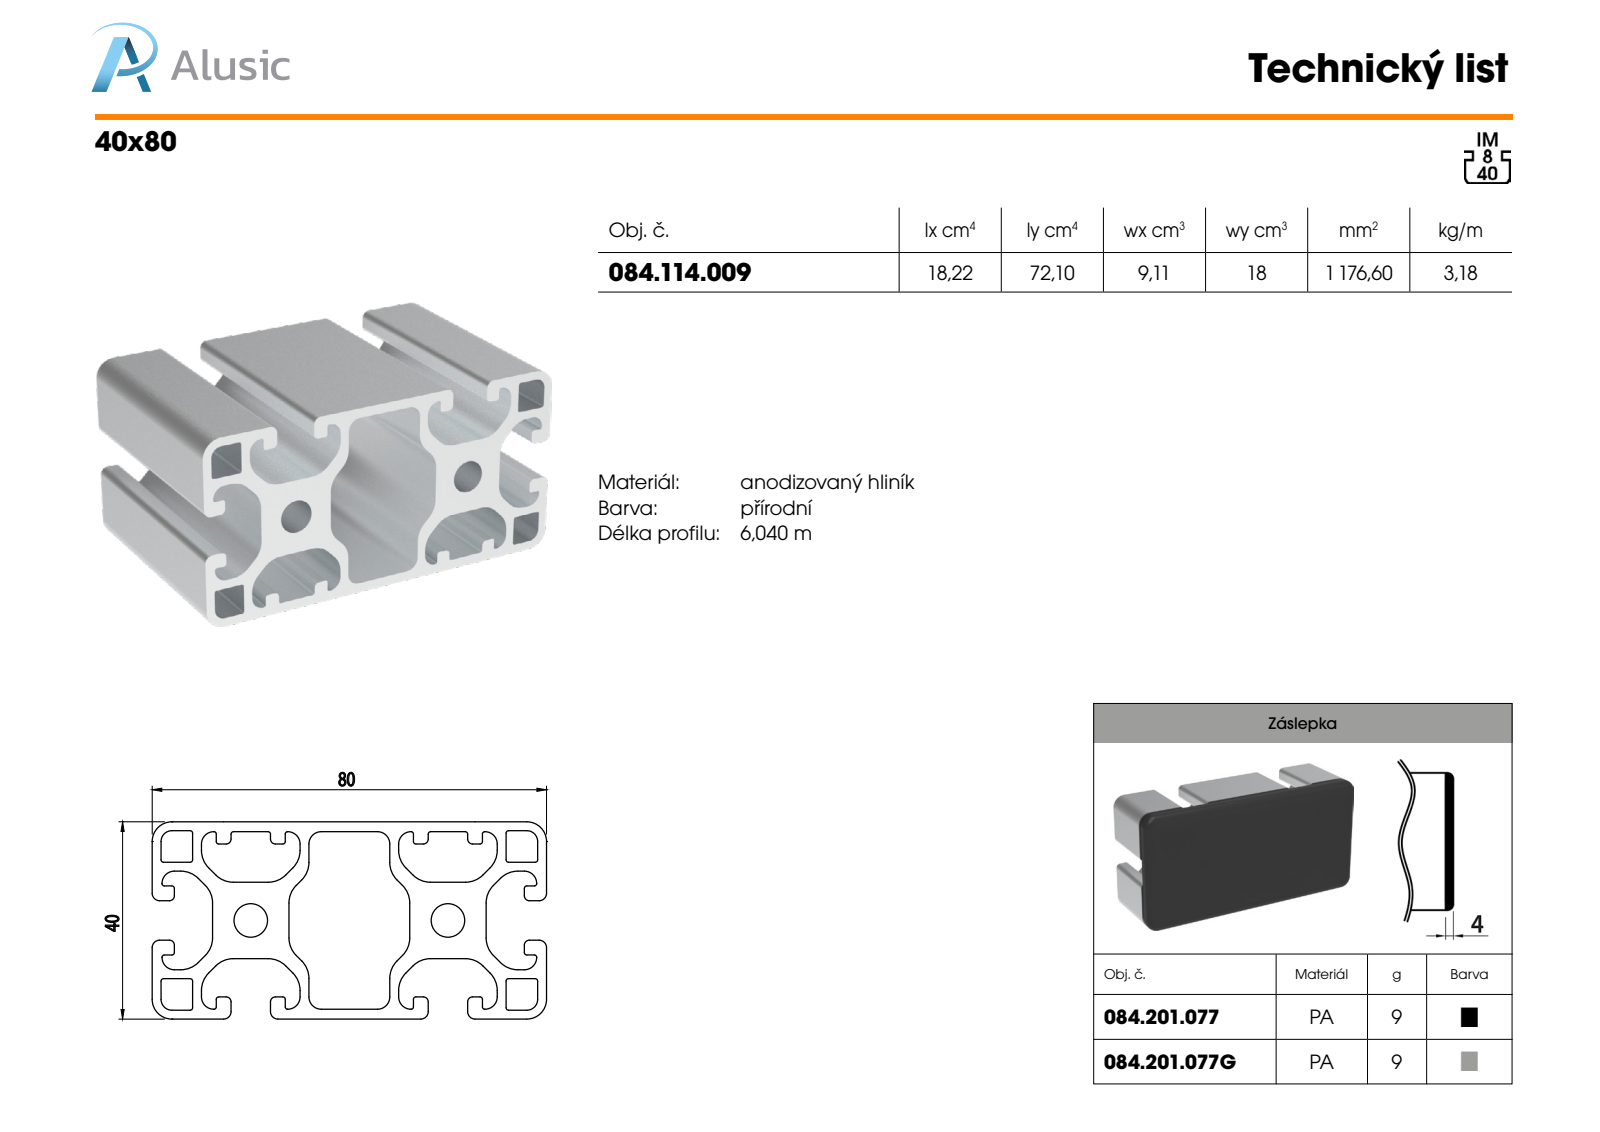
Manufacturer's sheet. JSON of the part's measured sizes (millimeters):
{"part_name": "084.114.009", "step_written_by": "SolidWorks 2018 (AUTOMOTIVE_DESIGN)", "units": "millimeters", "bodies": {"solids": 1, "faces": 238, "planar": 117, "cylindrical": 121, "other": 0}, "overall_size": [100, 80, 40], "volume_mm3": 117657, "surface_area_mm2": 81031, "round_holes": [[6.8, 2]], "partial_cylinders_radius": [[5, 32], [0.5, 28], [2.5, 16], [0.45, 12], [1, 12], [1.5, 8], [2.2, 4], [4, 4]], "face_to_face_distances": [40, 19.55, 4.05, 8.2, 27.75, 12.25, 2, 38, 31.8, 1.8], "hole_center_spacings": [40]}
